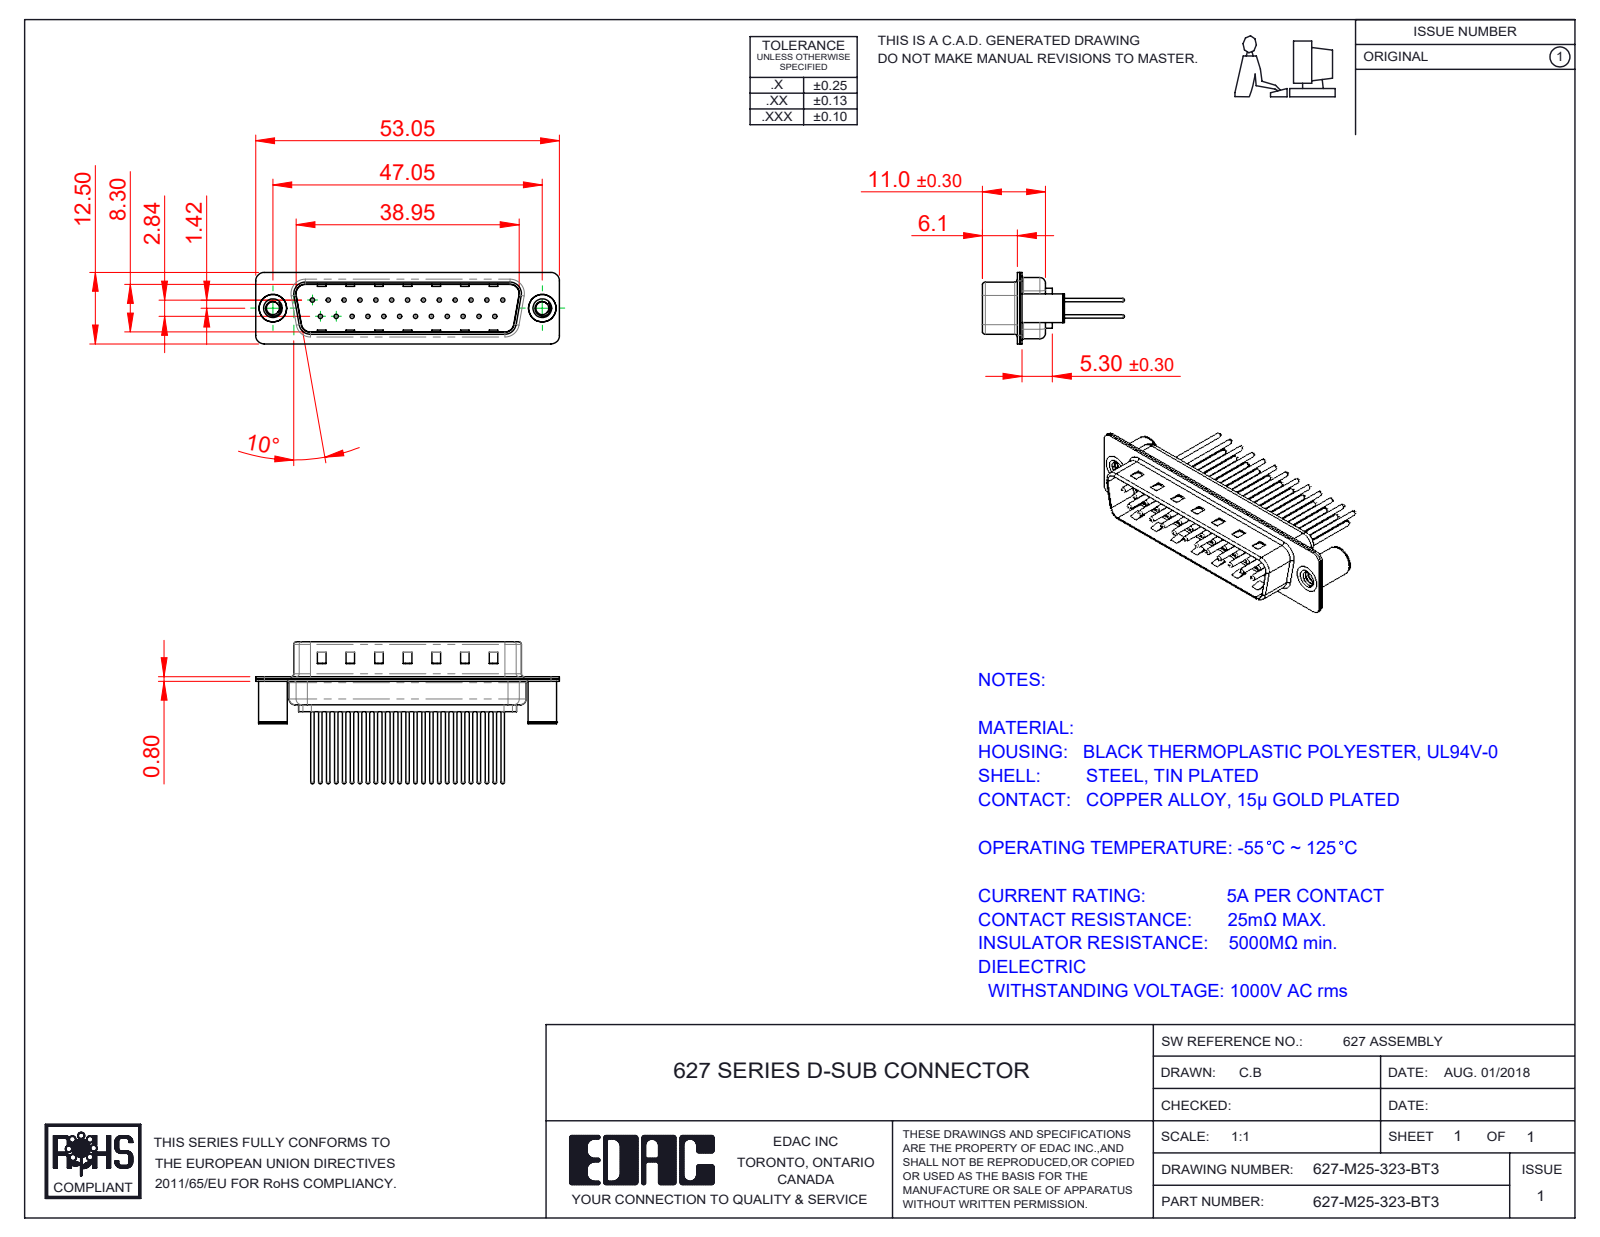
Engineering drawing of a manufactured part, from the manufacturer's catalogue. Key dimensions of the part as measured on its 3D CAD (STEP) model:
Part name (STEP PRODUCT): 627-M25-323-BT3; 627M Shell Front_25 Contacts; 627M Contact Row 1_23; 627M Contact Row 2_23 (+3 more)
STEP written by: SolidWorks 2020 (CONFIG_CONTROL_DESIGN)
Units: millimetres
Bodies: 30 solids, 1335 faces (346 planar, 511 cylindrical, 478 other)
Overall size (bounding box): 53.05 × 24.77 × 12.5
Volume: 2 890 mm³ · Surface area: 7 425 mm²
Round holes (diameter × count): ⌀0.75 ×25, ⌀1.6 ×25, ⌀2 ×25, ⌀2.26 ×2, ⌀3.26 ×2, ⌀4 ×2, ⌀4.8 ×2
Round bosses / shafts (diameter × count): ⌀1.5 ×25, ⌀0.6 ×25, ⌀5 ×2, ⌀4.9 ×2
Partial cylindrical surfaces — rounded edges, fillets, slot ends (radius × count): R1.5 ×16, R2 ×12, R0.5 ×8, R1.6 ×8, R0.25 ×4, R0.6 ×4, R0.65 ×4, R0.9 ×4
Main face-to-face distances: 0.4, 0.8, 9.5, 9.1, 8.7, 9.9, 1.2, 6.1, 5.7, 0.75
Hole centre spacings: 3.16, 2.77, 5.54, 8.31, 11.08, 13.85, 16.62, 5.03
